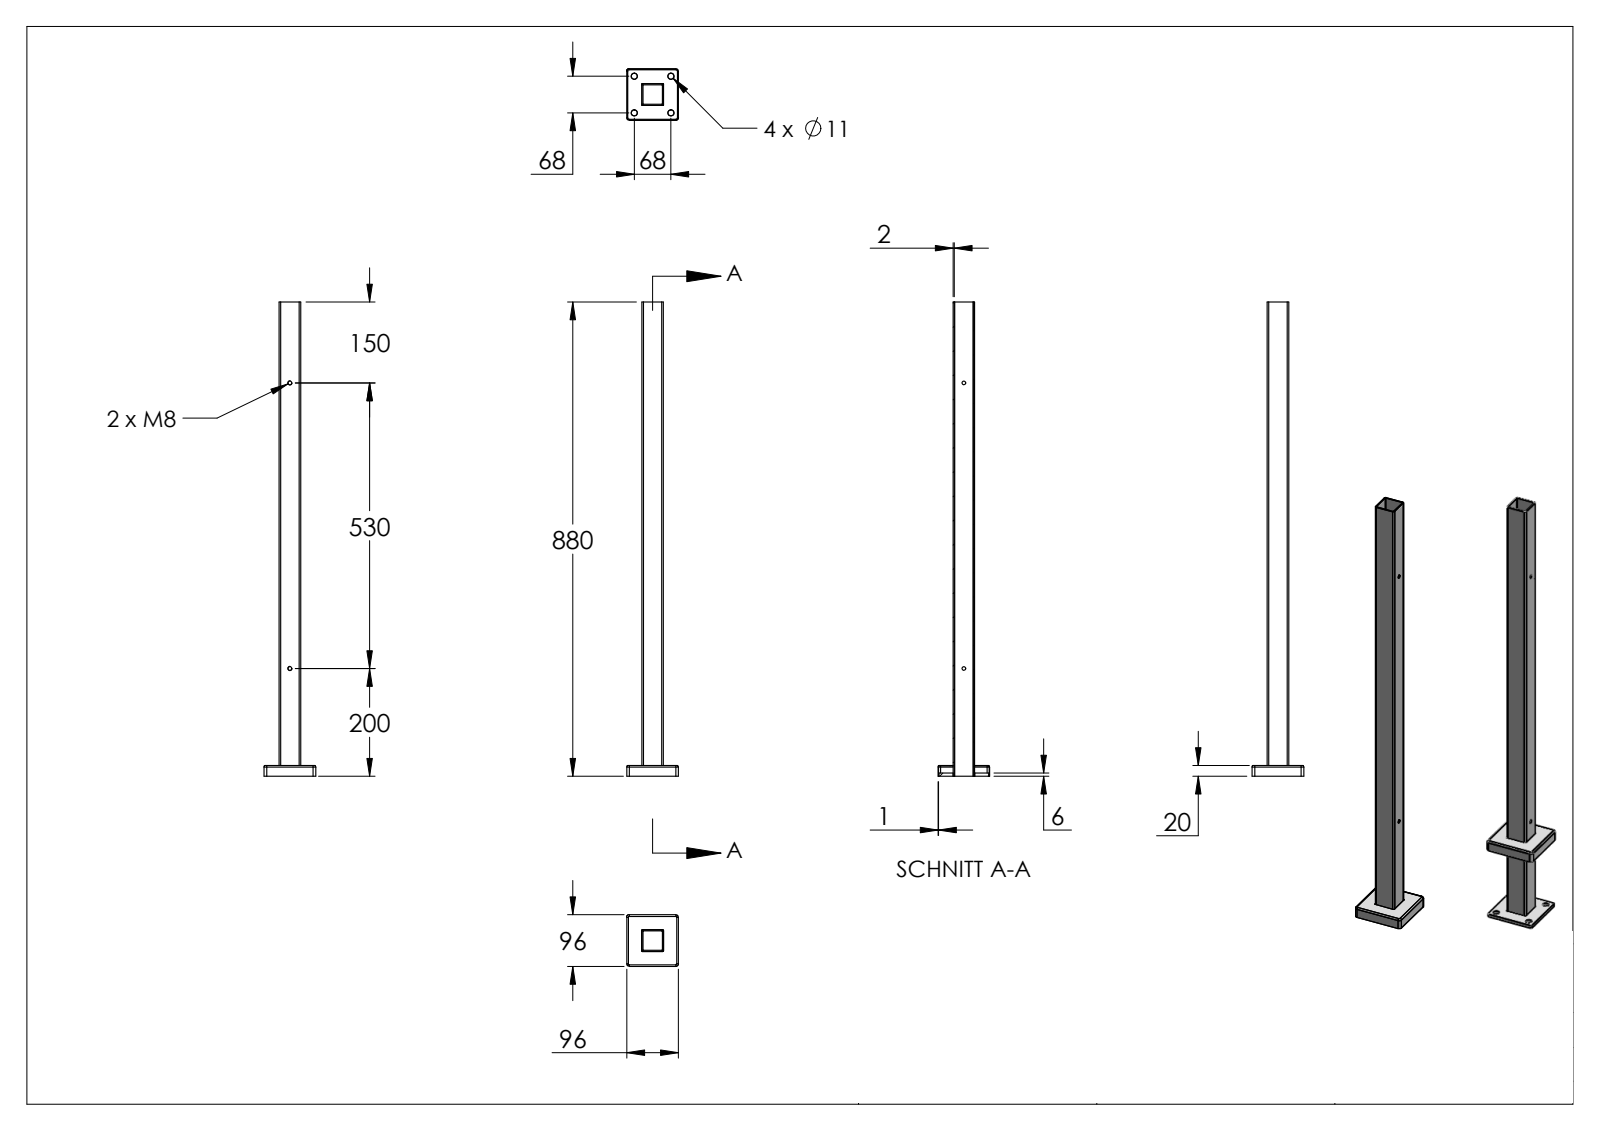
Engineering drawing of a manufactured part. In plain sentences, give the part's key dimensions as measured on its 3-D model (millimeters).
The part is named "40560-240; 51250-240_51250-240; 405XX-240 Teil1_40560-240 Teil1; 54208-240_54208-240". Its 3-D file was written by "SolidWorks 2015 (CONFIG_CONTROL_DESIGN)". It is 3 solids with 107 faces: 35 planar, 48 cylindrical and 24 other. Overall it measures 880 by 96 by 96 millimeters. Its volume is 314 337 cubic millimeters and its surface area 307 865 square millimeters. Round holes: 4 of diameter 11, 2 of diameter 6.8. Partial cylindrical surfaces (rounded edges, fillets, slot ends): 8 of radius 2, 8 of radius 3, 4 of radius 0.5, 4 of radius 1, 4 of radius 1.5, 4 of radius 4, 4 of radius 5. The main face-to-face distances are 2, 38, 40, 36, 1, 28, 66, 19, 20, 6. The hole center spacings are 68, 96.17, 530.
